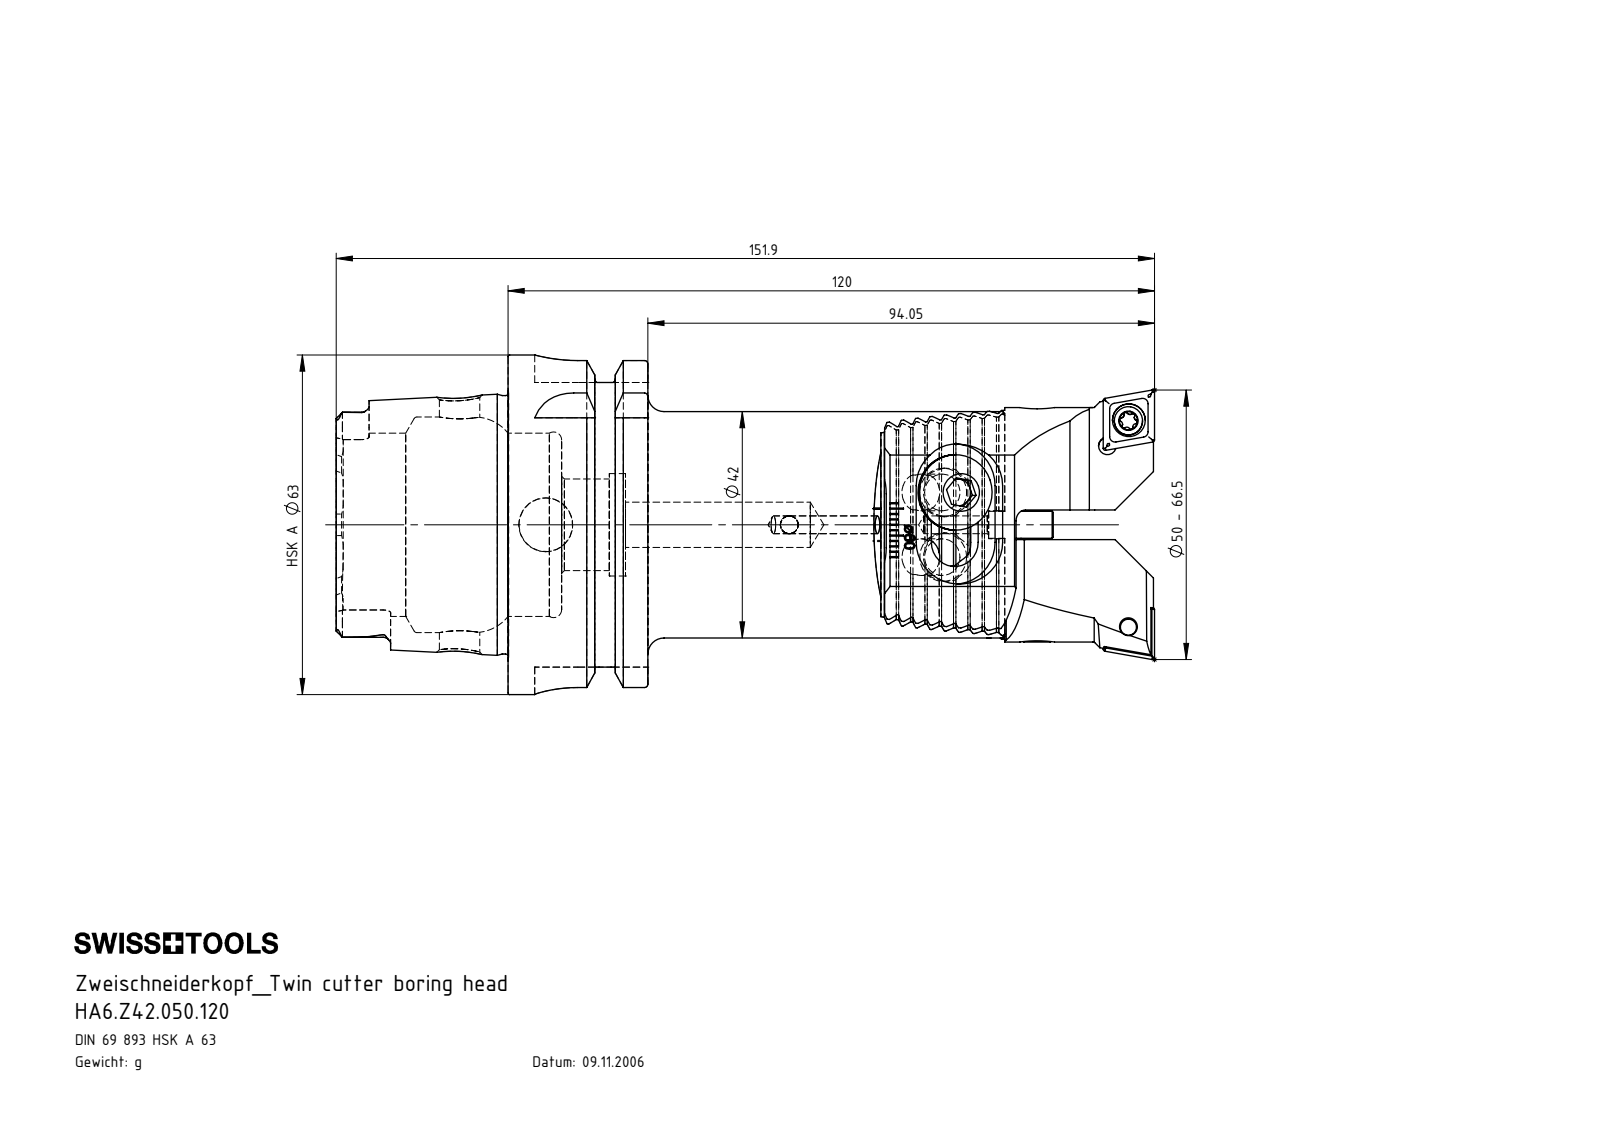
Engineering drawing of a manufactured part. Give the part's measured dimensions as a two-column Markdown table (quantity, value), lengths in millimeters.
| quantity | value |
| --- | --- |
| part name | Z42-ER2.001.019_A; Z42-ER1.003.020_A_gespannt; HA6.Z42.K23.120; Z42-ER1.001.020 (+2 more) |
| STEP written by | SolidWorks 2017 (AUTOMOTIVE_DESIGN) |
| units | millimeters |
| bodies | 6 solids, 370 faces (204 planar, 88 cylindrical, 78 other) |
| overall size | 133.1 × 63 × 63 |
| volume | 156 210 mm³ |
| surface area | 35 928 mm² |
| round holes (diameter × count) | 3.3 × 4, 8.4 × 3, 6.8 × 2, 9 × 2, 3 × 1, 7.5 × 1, 10 × 1, 17 × 1, 19 × 1, 34 × 1, 40 × 1 |
| round bosses / shafts (diameter × count) | 14 × 2, 8 × 2, 63 × 1, 54.95 × 1, 47.94 × 1, 42 × 1, 5 × 1, 4 × 1 |
| partial cylindrical surfaces (radius × count) | 0.2 × 18, 1.4 × 6, 2.88 × 4, 8 × 4, 220 × 2 |
| main face-to-face distances | 2.38, 4.76, 25.95, 11.91, 9.53, 7.15, 14.29, 16, 7.14, 9.95 |
| hole center spacings | 45.2 |
